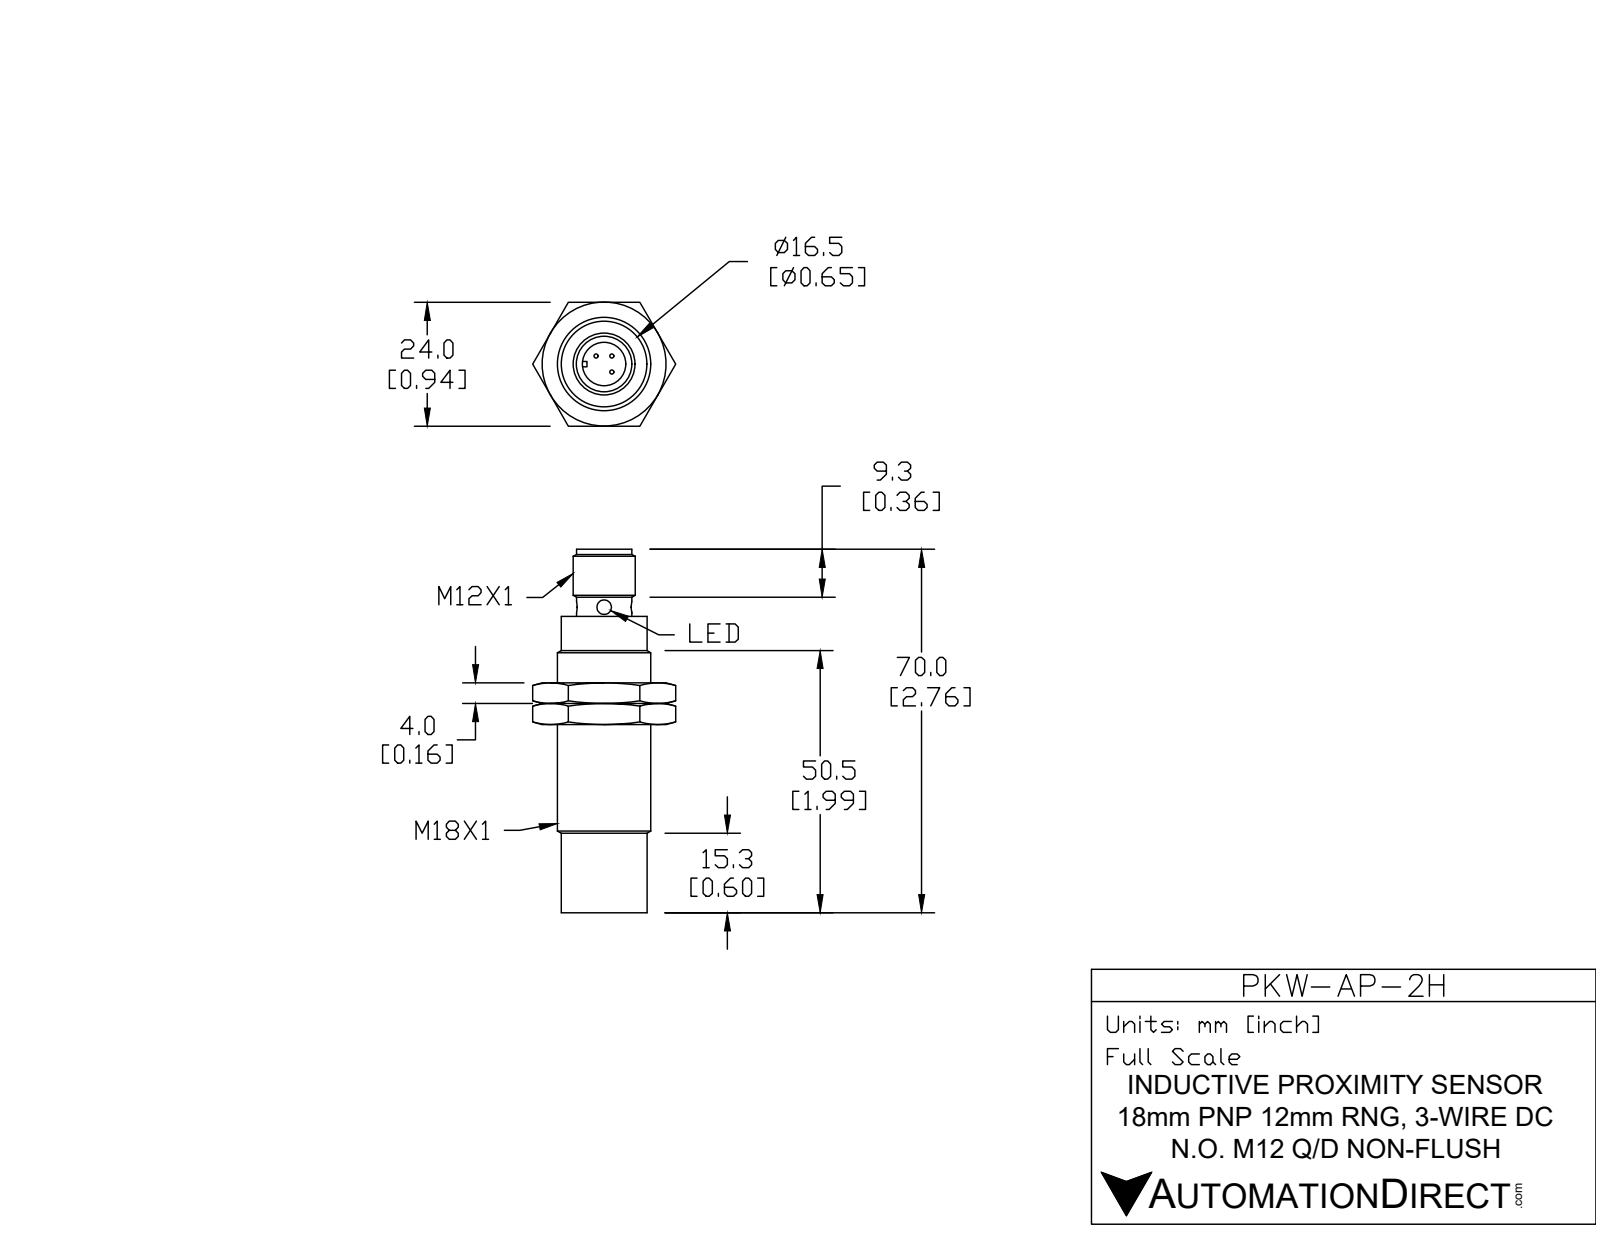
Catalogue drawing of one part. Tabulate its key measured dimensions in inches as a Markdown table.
| quantity | value |
| --- | --- |
| part name | PKW-AP-2H |
| STEP written by | SolidWorks 2017 (AUTOMOTIVE_DESIGN) |
| units | inches |
| bodies | 3 solids, 124 faces (26 planar, 27 cylindrical, 71 other) |
| overall size | 2.764 × 1.091 × 0.945 |
| volume | 1.015 in³ |
| surface area | 9.927 in² |
| round holes (diameter × count) | 0.118 × 2, 0.331 × 1, 0.666 × 1 |
| round bosses / shafts (diameter × count) | 0.709 × 1, 0.654 × 1, 0.652 × 1, 0.472 × 1, 0.445 × 1, 0.417 × 1 |
| partial cylindrical surfaces (radius × count) | 0.024 × 1 |
| main face-to-face distances | 0.157, 0.945, 0.953, 0.315, 1.11, 0.795, 1.299, 1.457, 1.142, 2.252 |
